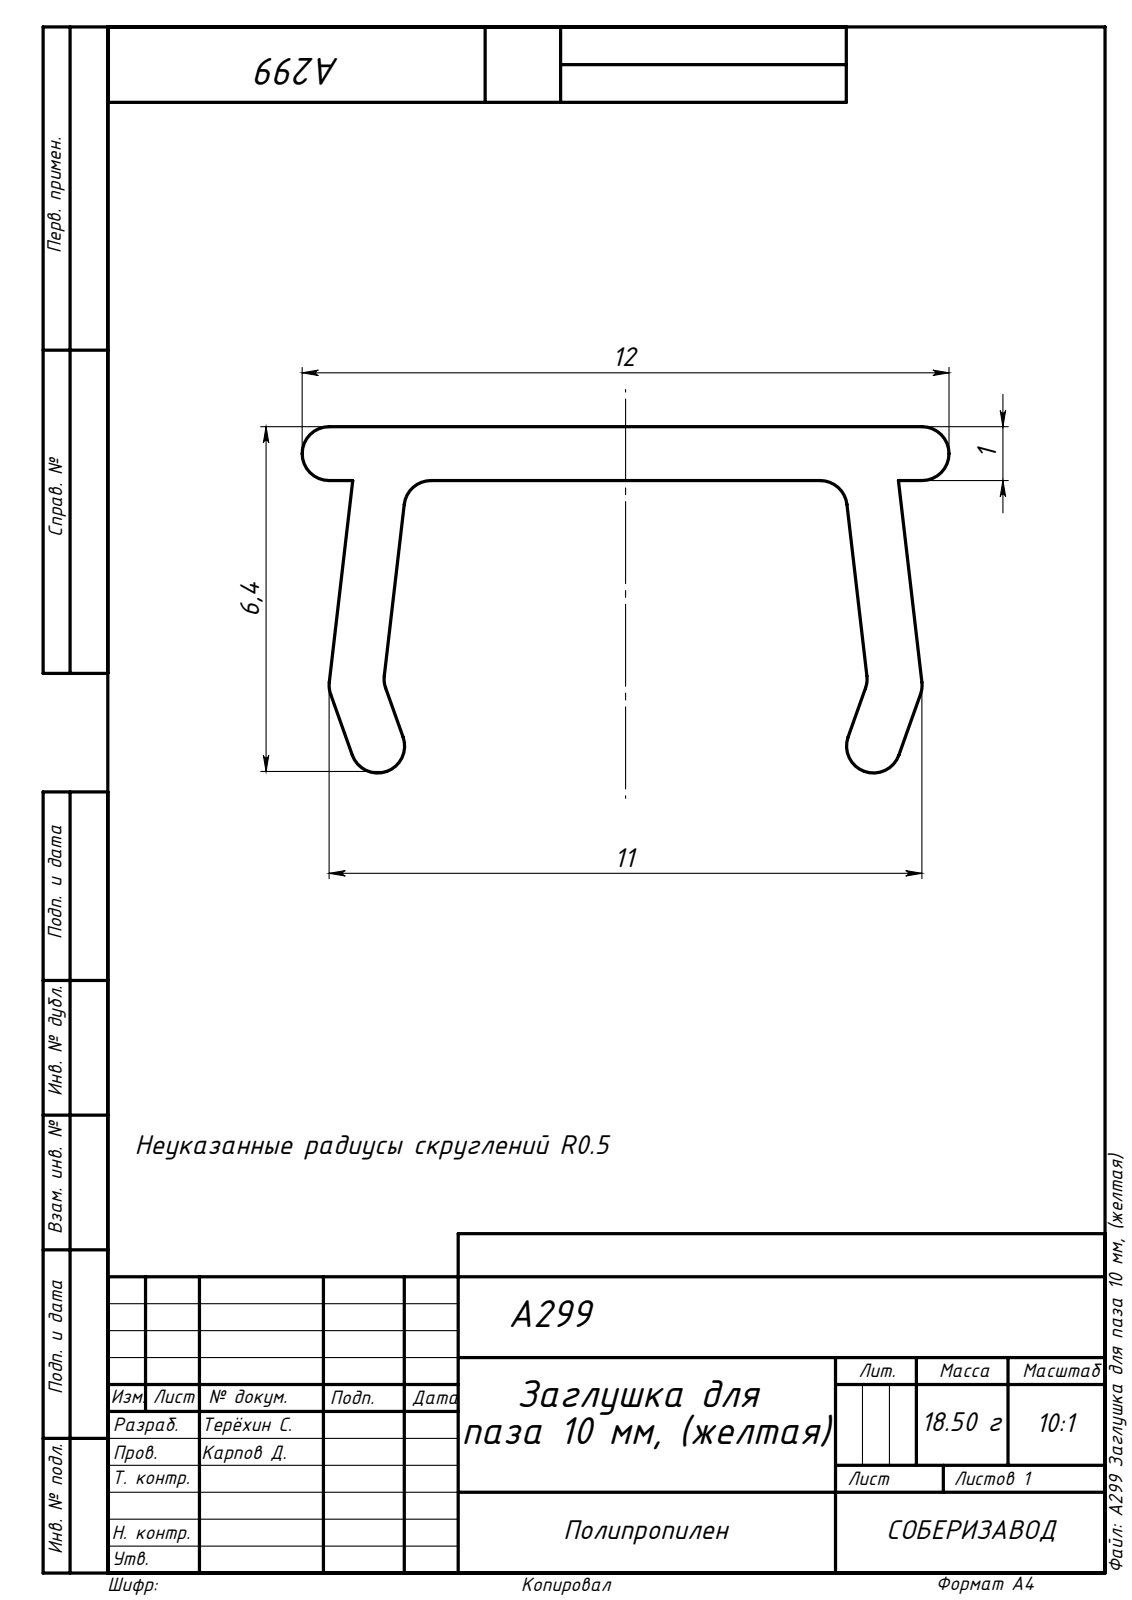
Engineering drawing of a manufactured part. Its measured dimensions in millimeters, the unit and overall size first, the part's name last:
Units: millimetres
Overall size (bounding box): 1000 × 12 × 6.43
Partial cylindrical surfaces — rounded edges, fillets, slot ends (radius × count): R0.5 ×10
Main face-to-face distances: 1, 1000
Volume: 22 699 mm³ · Surface area: 46 067 mm²
Bodies: 1 solid, 30 faces (14 planar, 16 cylindrical, 0 other)
Part name (STEP PRODUCT): A300 Заглушка для паза 10 мм, (темно-серая)
STEP written by: SolidWorks 2019 (AUTOMOTIVE_DESIGN)
